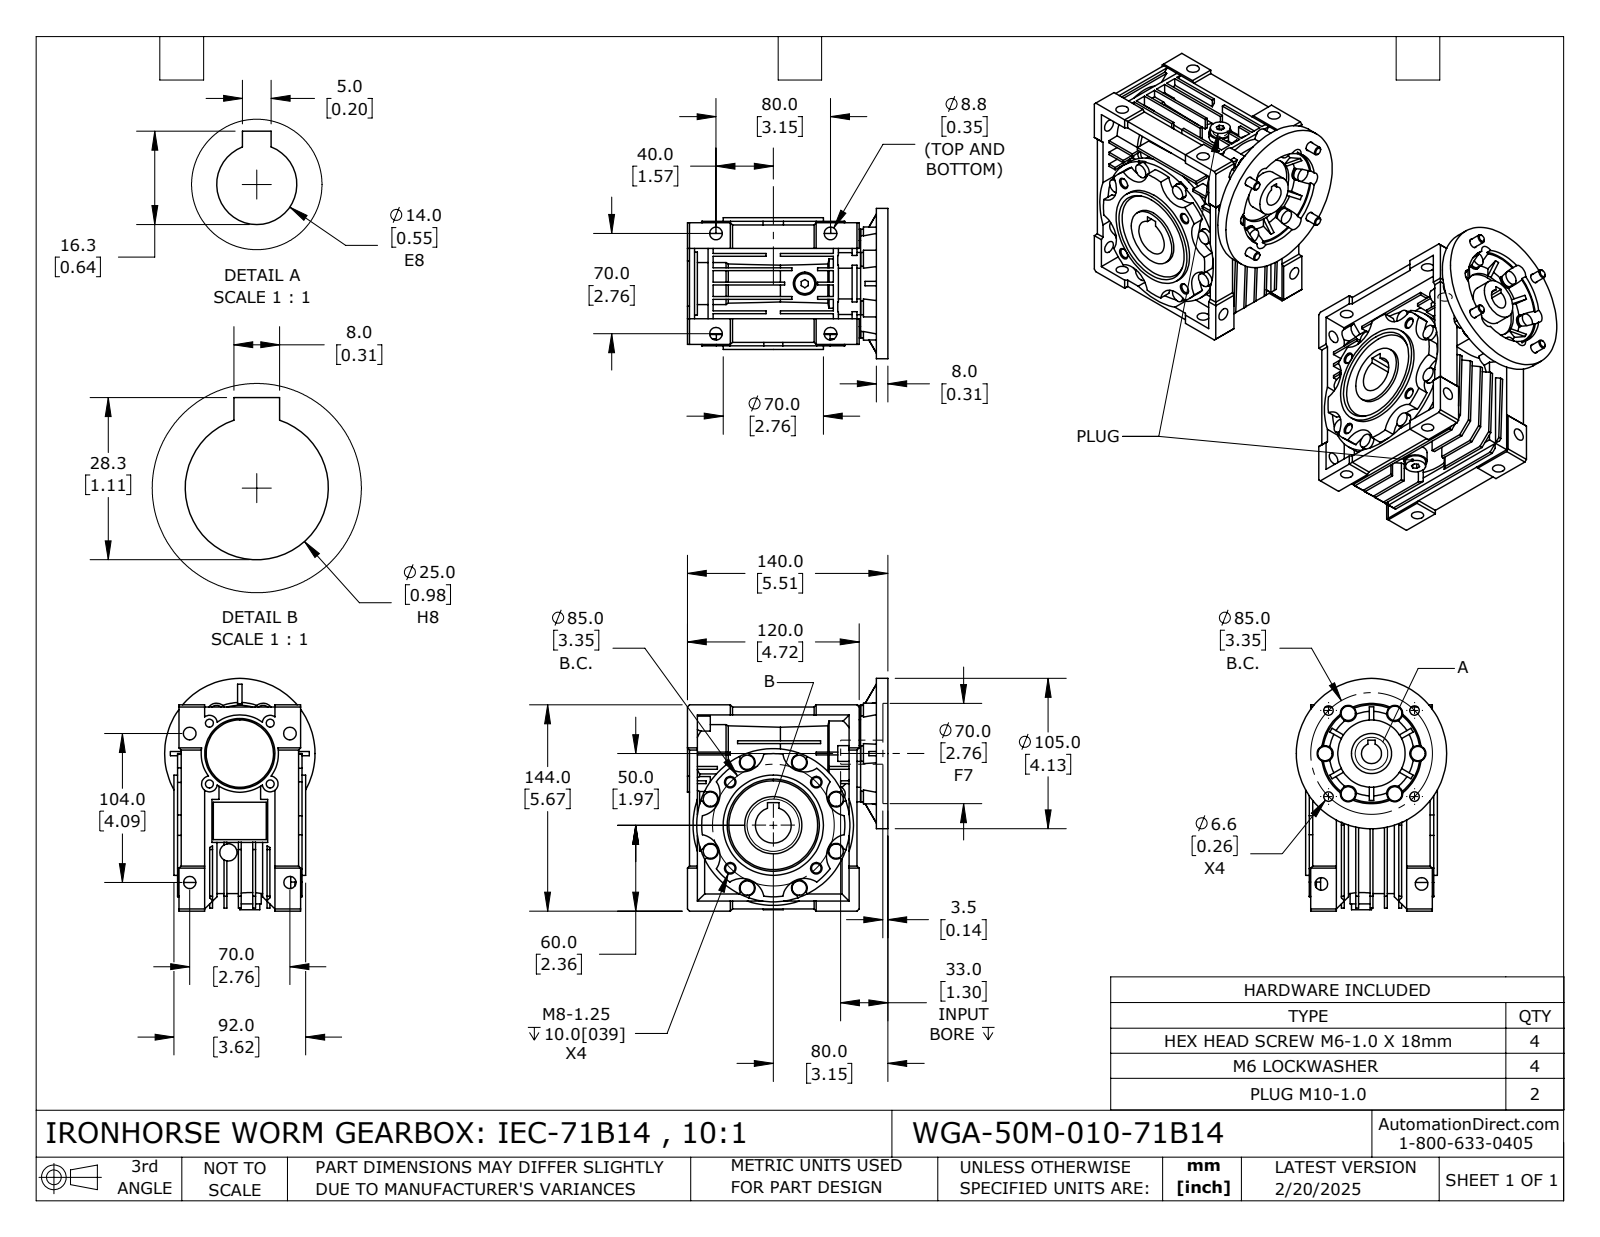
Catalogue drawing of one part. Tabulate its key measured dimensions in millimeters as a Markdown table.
| quantity | value |
| --- | --- |
| part name | WGA-50M-010-71B14 |
| STEP written by | SolidWorks 2024 (CONFIG_CONTROL_DESIGN) |
| units | millimeters |
| bodies | 15 solids, 1132 faces (615 planar, 372 cylindrical, 145 other) |
| overall size | 162.5 × 148.5 × 105 |
| volume | 1 065 000 mm³ |
| surface area | 235 209 mm² |
| round holes (diameter × count) | 8.8 × 8, 8.5 × 6, 5.55 × 4, 6.1 × 4, 6.6 × 4, 6.65 × 2, 6.65 × 2, 9 × 2, 14 × 1, 15 × 1, 25 × 1, 28 × 1 |
| round bosses / shafts (diameter × count) | 10 × 14, 12.2 × 4, 6 × 4, 16 × 2, 14 × 2, 9.8 × 2, 8.3 × 2, 107 × 1 |
| partial cylindrical surfaces (radius × count) | 5.5 × 18, 6 × 8, 15 × 8, 15.5 × 8, 5.75 × 6, 7 × 6, 20.76 × 1, 35 × 1 |
| main face-to-face distances | 8, 2, 10, 7, 1.5, 5.5, 20, 12, 55, 35 |
| hole center spacings | 42.5, 52.02, 60.1, 70, 12.5, 30, 42.42, 72.49 |
